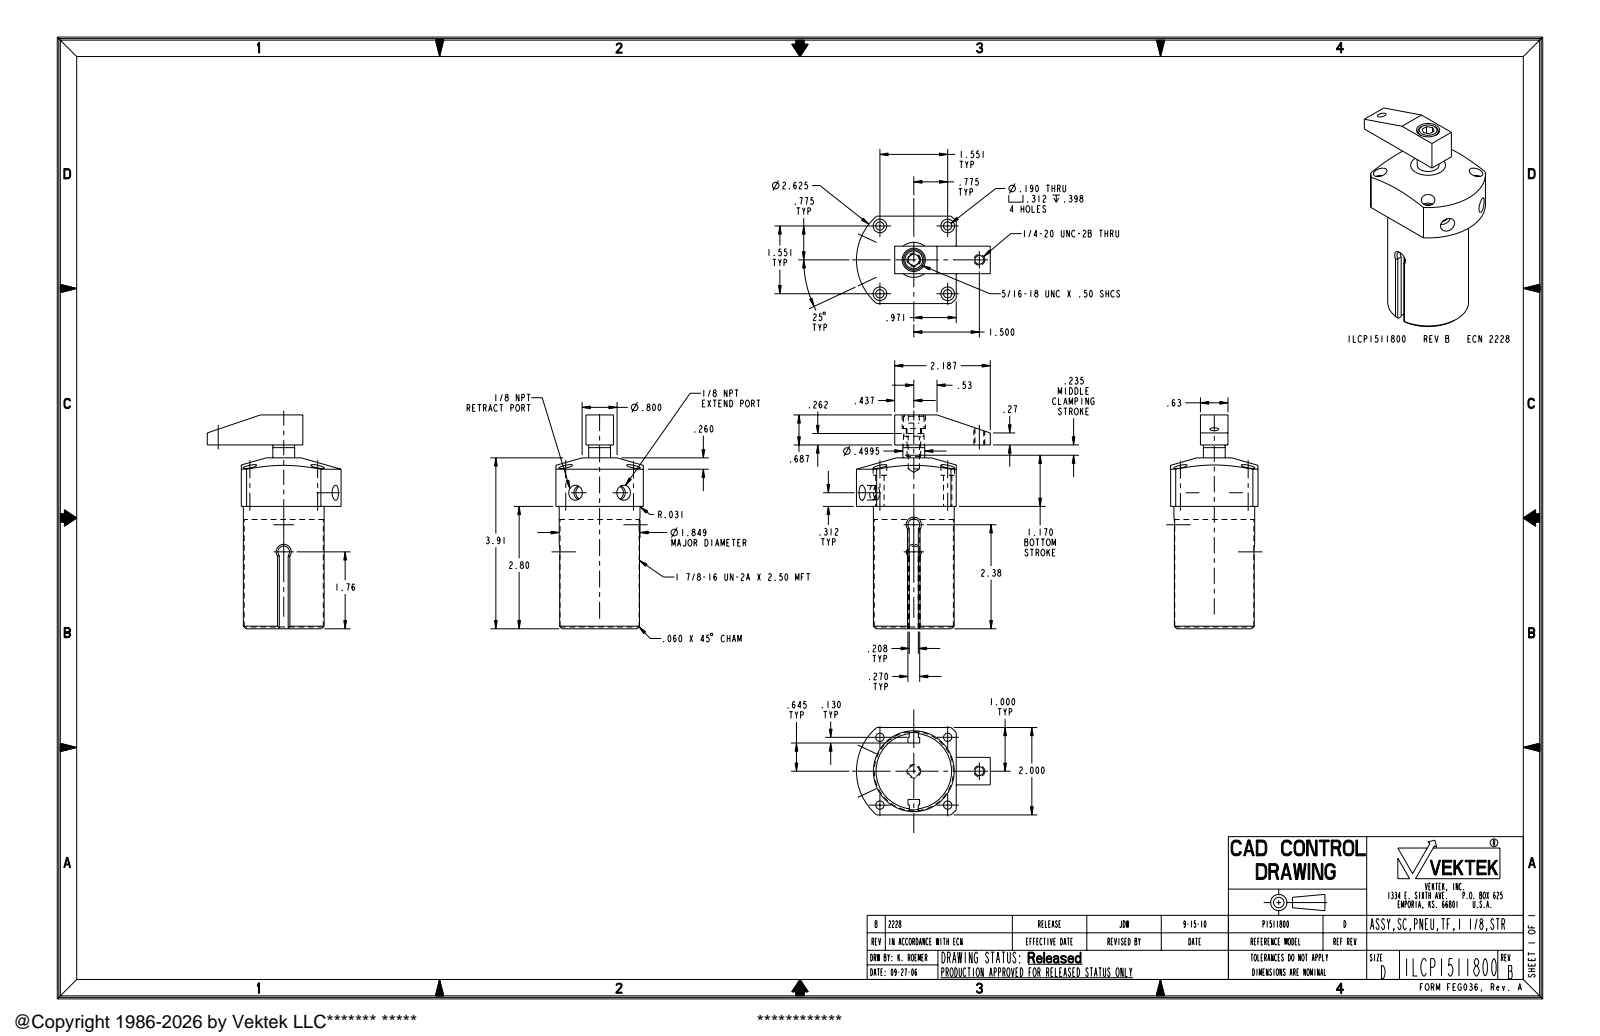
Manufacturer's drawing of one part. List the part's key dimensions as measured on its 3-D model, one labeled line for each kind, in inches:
Part name (STEP PRODUCT): ILCP1511800; ILC91500903; ILCP1511800_ASM
STEP written by: PRO/ENGINEER BY PARAMETRIC TECHNOLOGY CORPORATION, 2007460 (AUTOMOTIVE_DESIGN_CC2)
Units: inches
Bodies: 2 solids, 123 faces (52 planar, 47 cylindrical, 24 other)
Overall size (bounding box): 4.892 × 3.063 × 2
Volume: 12.02 in³ · Surface area: 61.38 in²
Round holes (diameter × count): ⌀0.19 ×4, ⌀0.312 ×4, ⌀0.328 ×2, ⌀0.201 ×1, ⌀0.257 ×1, ⌀0.344 ×1, ⌀0.531 ×1
Round bosses / shafts (diameter × count): ⌀1.849 ×1, ⌀1.812 ×1, ⌀0.5 ×1, ⌀0.469 ×1, ⌀0.312 ×1, ⌀0.25 ×1
Partial cylindrical surfaces — rounded edges, fillets, slot ends (radius × count): R0.132 ×1, R0.135 ×1, R1.312 ×1
Main face-to-face distances: 0.687, 2, 2.8, 1.317, 0.683, 0.63, 1.313, 0.355, 1.645, 1.405
Hole centre spacings: 1.096, 1.55, 1.061, 2.193, 2.404, 1.5
